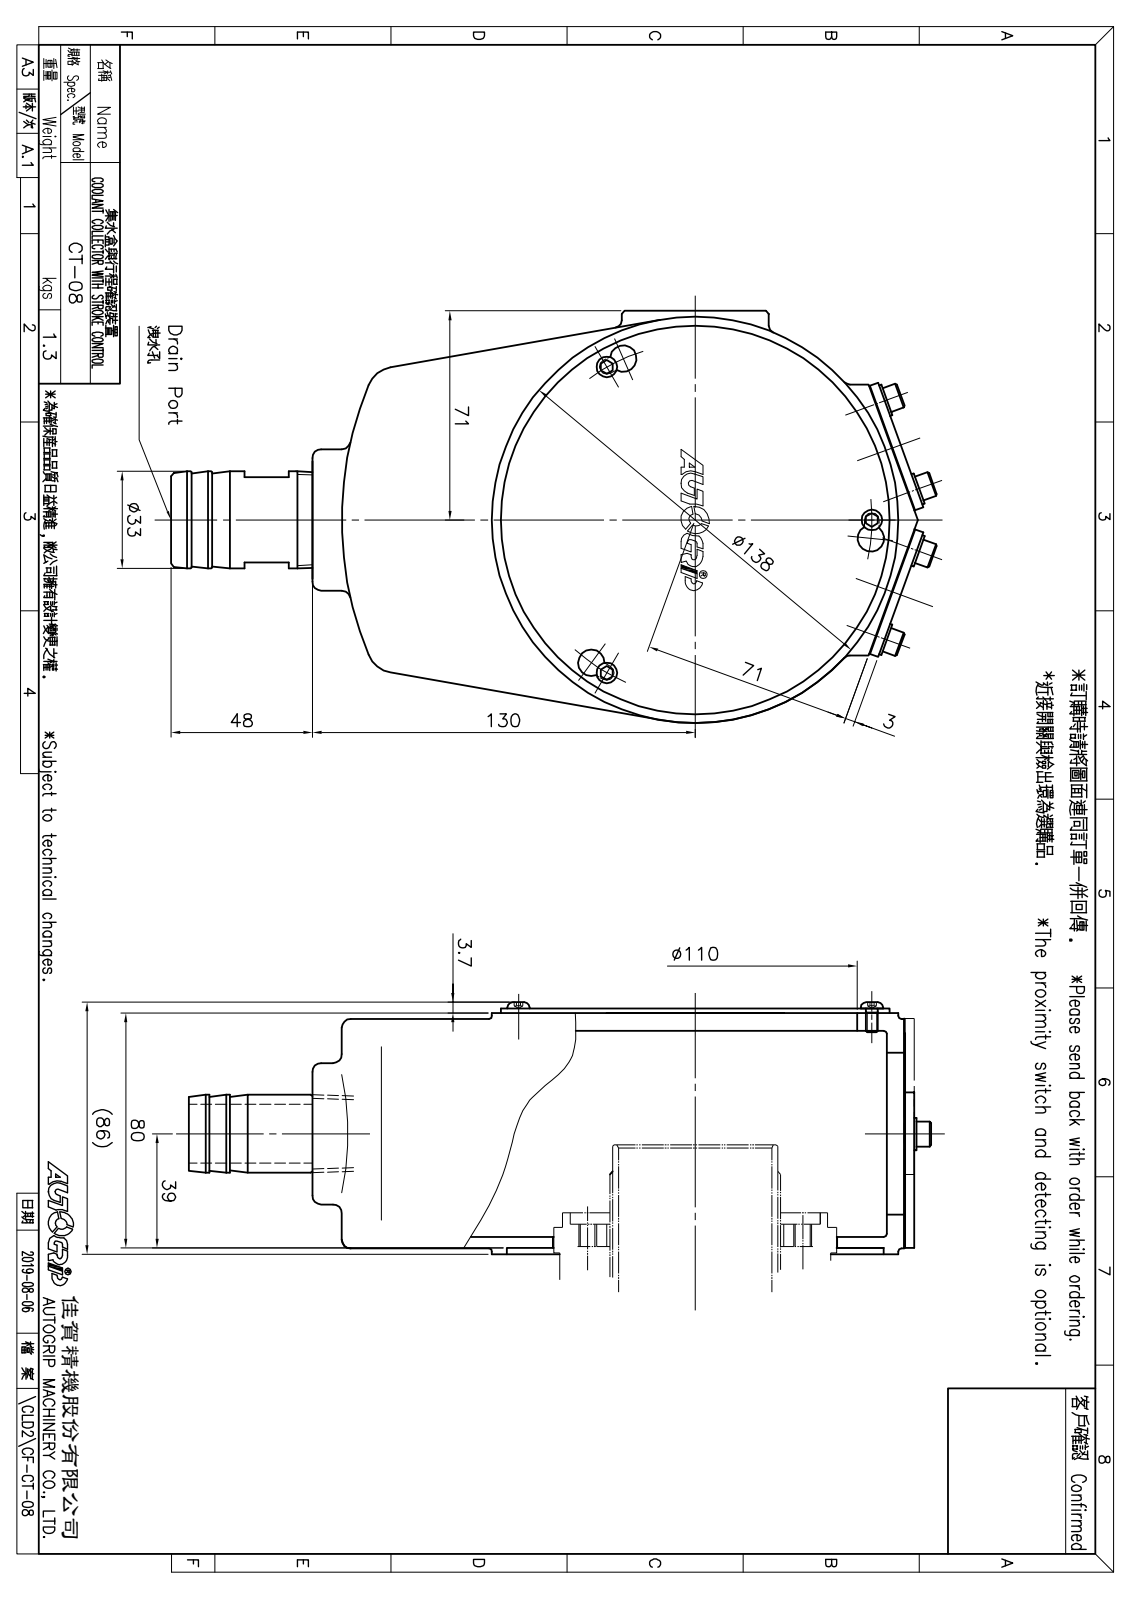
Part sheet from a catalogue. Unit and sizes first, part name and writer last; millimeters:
Units: millimetres
Overall size (bounding box): 258.35 × 140 × 85.5
Round holes (diameter × count): ⌀5 ×4, ⌀4 ×3, ⌀12 ×2, ⌀25 ×1, ⌀96.5 ×1, ⌀128 ×1
Round bosses / shafts (diameter × count): ⌀8.5 ×4, ⌀7 ×3, ⌀5 ×2, ⌀138 ×1, ⌀132 ×1, ⌀45 ×1, ⌀33 ×1
Partial cylindrical surfaces — rounded edges, fillets, slot ends (radius × count): R2.75 ×16, R3 ×10, R7 ×8, R2 ×6, R2.5 ×2, R6 ×2, R10 ×2, R65 ×1
Main face-to-face distances: 4, 6, 7.5, 1.5, 76, 74, 70, 77.5, 0.5, 2
Hole centre spacings: 60, 103.92, 20.59, 20.6, 32
Volume: 410 603 mm³ · Surface area: 209 608 mm²
Bodies: 14 solids, 412 faces (204 planar, 115 cylindrical, 93 other)
Part name (STEP PRODUCT): CF-CT-08; M5x8; CT-08洩油管; CT-08集水盒本體
STEP written by: SolidWorks 2016 (CONFIG_CONTROL_DESIGN)
